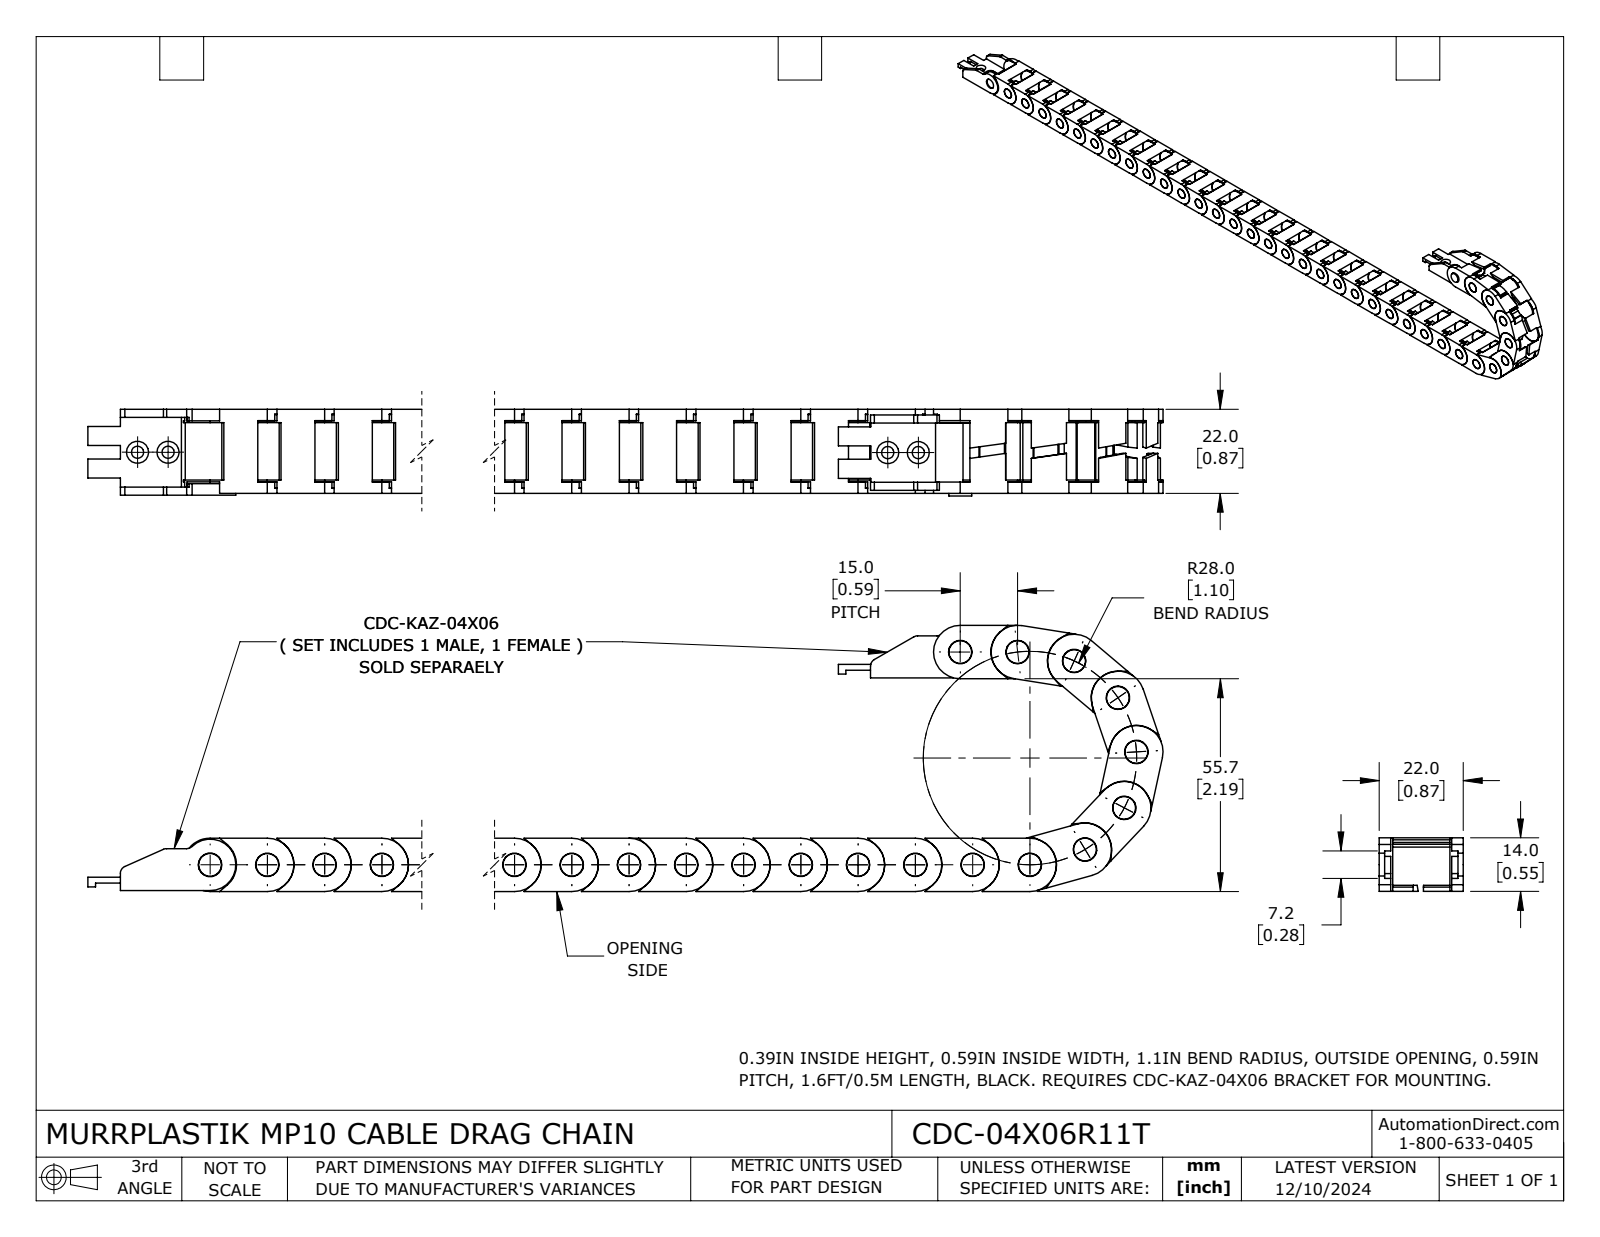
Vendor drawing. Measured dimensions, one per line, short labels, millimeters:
name: CDC-04X06R11T
written by: SolidWorks 2024 (AUTOMOTIVE_DESIGN)
unit: mm
bodies: 36 solids, 2455 faces (1666 planar, 785 cylindrical, 4 other)
size: 486.9 × 69.7 × 22.7
volume: 65 020 mm³; area: 91 290 mm²
holes: 34× ⌀6.1, 4× ⌀3.2, 1× ⌀6.2
bosses: 35× ⌀6, 28× ⌀14
rounds: 170× R0.5, 40× R7, 34× R3.6, 34× R11.6, 12× R7, 6× R2, 2× R1, 2× R6.8
face distances: 3.5, 18.5, 22, 1.6, 14, 15, 2.2, 0.5, 1.3, 17.7
hole spacings: 15, 30, 45, 60, 75, 90, 105, 120
